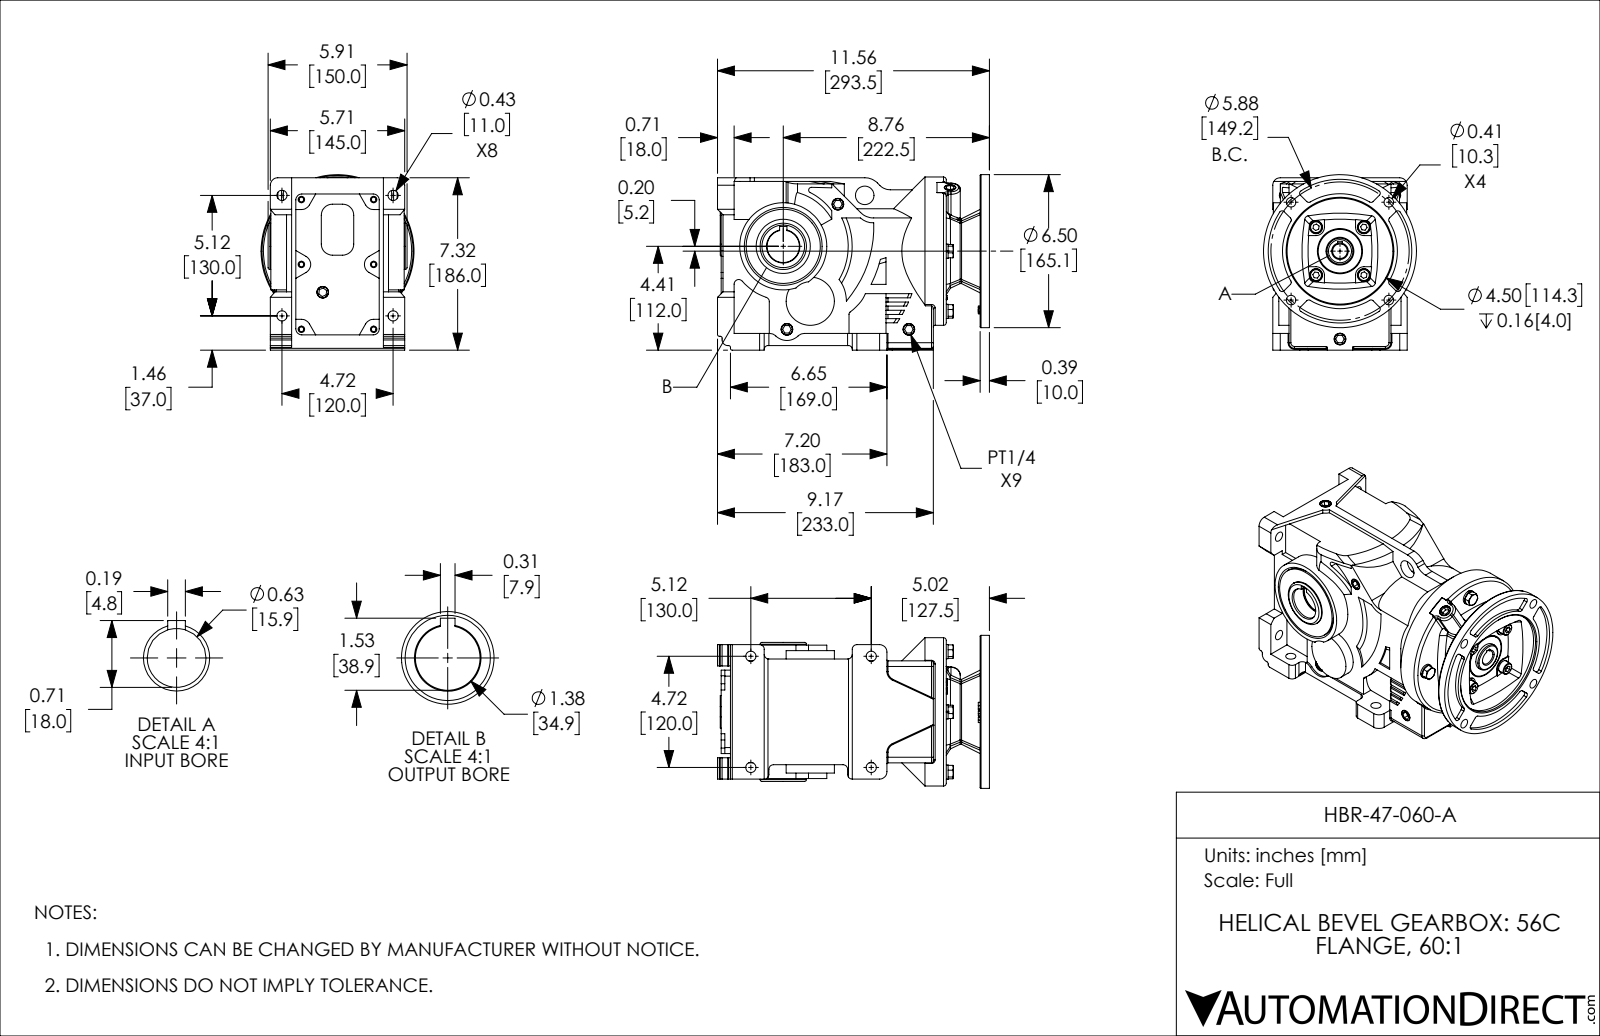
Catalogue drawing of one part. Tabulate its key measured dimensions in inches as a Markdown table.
| quantity | value |
| --- | --- |
| part name | HBR-47-060-A |
| STEP written by | SolidWorks 2018 (AUTOMOTIVE_DESIGN) |
| units | inches |
| bodies | 1 solid, 1002 faces (447 planar, 317 cylindrical, 238 other) |
| overall size | 11.555 × 7.455 × 6.5 |
| volume | 308.7 in³ |
| surface area | 495.3 in² |
| round holes (diameter × count) | 0.433 × 8, 0.197 × 6, 0.276 × 6, 0.323 × 4, 0.354 × 4, 0.406 × 4, 0.551 × 4, 0.625 × 1, 0.787 × 1, 0.846 × 1, 1.375 × 1, 1.457 × 1 |
| round bosses / shafts (diameter × count) | 0.606 × 4, 0.512 × 4, 0.315 × 4, 6.5 × 1, 6.299 × 1, 3.701 × 1, 3.15 × 1, 2.047 × 1 |
| partial cylindrical surfaces (radius × count) | 0.118 × 22, 0.079 × 18, 0.394 × 12, 0.197 × 10, 0.472 × 9, 0.039 × 5, 0.256 × 4, 0.315 × 4 |
| main face-to-face distances | 0.197, 0.394, 0.236, 0.157, 11.004, 4.331, 0.118, 0.079, 11.24, 10.846 |
| hole center spacings | 1.848, 2.132, 3.27, 3.717, 5.08, 5.118, 1.437, 1.5 |
